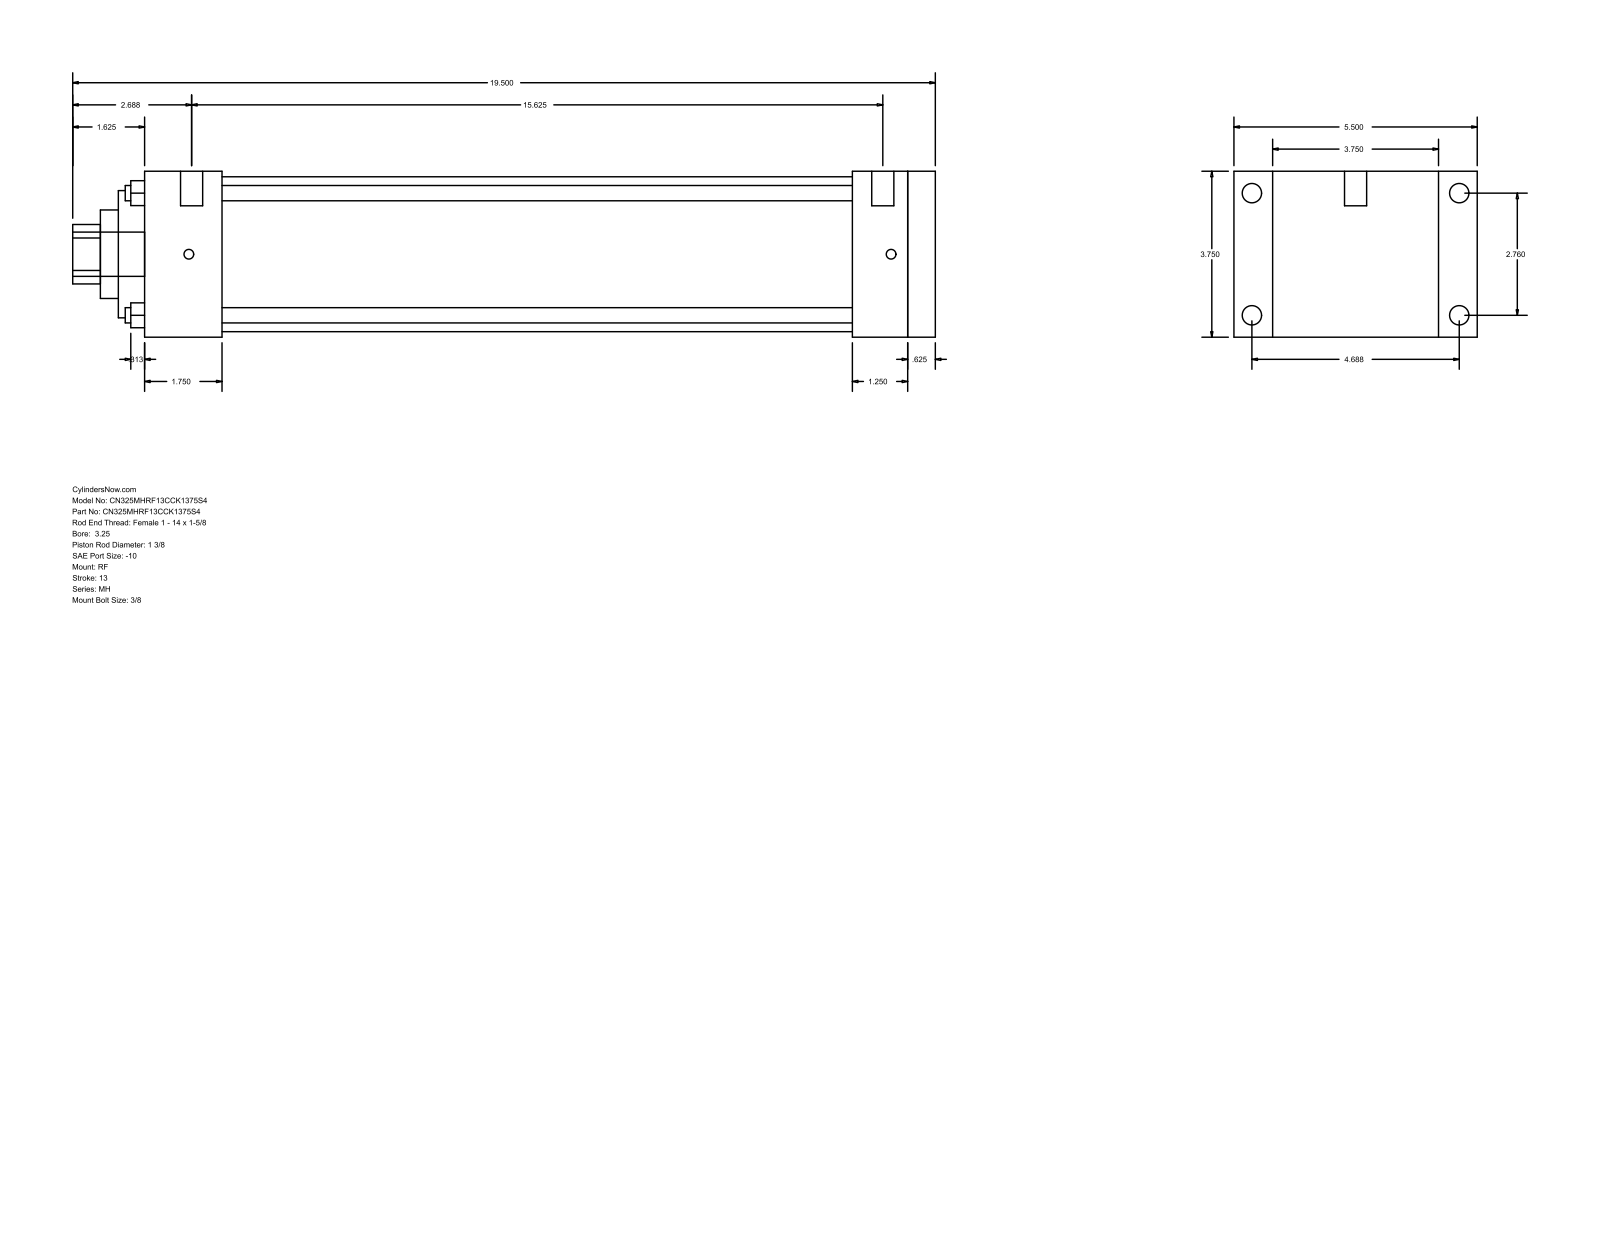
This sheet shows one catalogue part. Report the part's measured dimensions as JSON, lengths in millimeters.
{"part_name": "MH_RF__0325_1.375", "step_written_by": "GSSL Pune (CONFIG_CONTROL_DESIGN)", "units": "millimeters", "bodies": {"solids": 0, "faces": 94, "planar": 65, "cylindrical": 29, "other": 0}, "overall_size": [495.3, 139.7, 95.25], "round_holes": [[8.76, 4], [34.92, 1], [50.8, 1], [73.03, 1], [88.9, 1]], "round_bosses_or_shafts": [[11.13, 4], [5.56, 4], [12.7, 2], [25.4, 1]], "partial_cylinders_radius": [[17.06, 1]], "face_to_face_distances": [95.24, 454.03, 438.16, 15.87, 22.23, 117.47, 44.45, 393.71, 409.58, 406.41], "hole_center_spacings": [49.57, 70.1, 99.14]}
